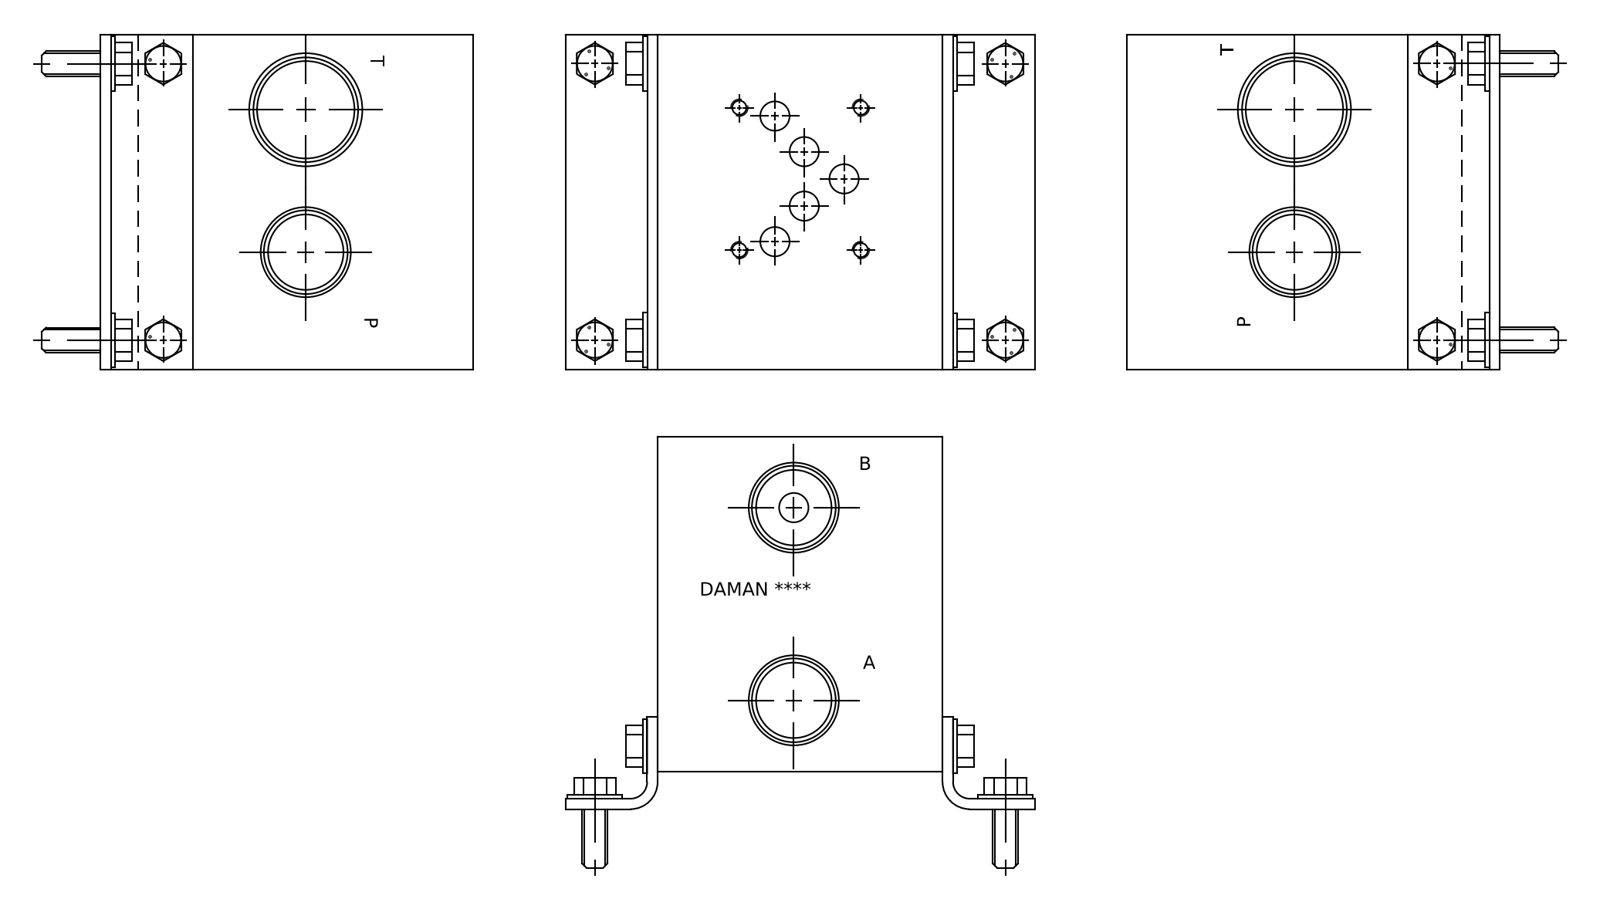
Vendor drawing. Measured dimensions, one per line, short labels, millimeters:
name: Part_AD05JP013P_3D
written by: Autodesk Inventor 2021 (AUTOMOTIVE_DESIGN)
unit: mm
bodies: 1 solid, 388 faces (242 planar, 33 cylindrical, 113 other)
size: 127 × 127 × 107.95
volume: 1 588 000 mm³; area: 106 765 mm²
holes: 4× ⌀5.11, 4× ⌀6.35, 3× ⌀9.53, 3× ⌀28.57, 3× ⌀33.71, 2× ⌀7.92, 2× ⌀10.31, 2× ⌀11.13, 1× ⌀36.91, 1× ⌀42.47
face distances: 127, 107.95, 19, 19.51, 88.44, 0.51, 108, 88.95, 69.44, 68.93
hole spacings: 17.48, 18.28, 35.4, 35.89, 13.86, 13.87, 20.64, 27.15
